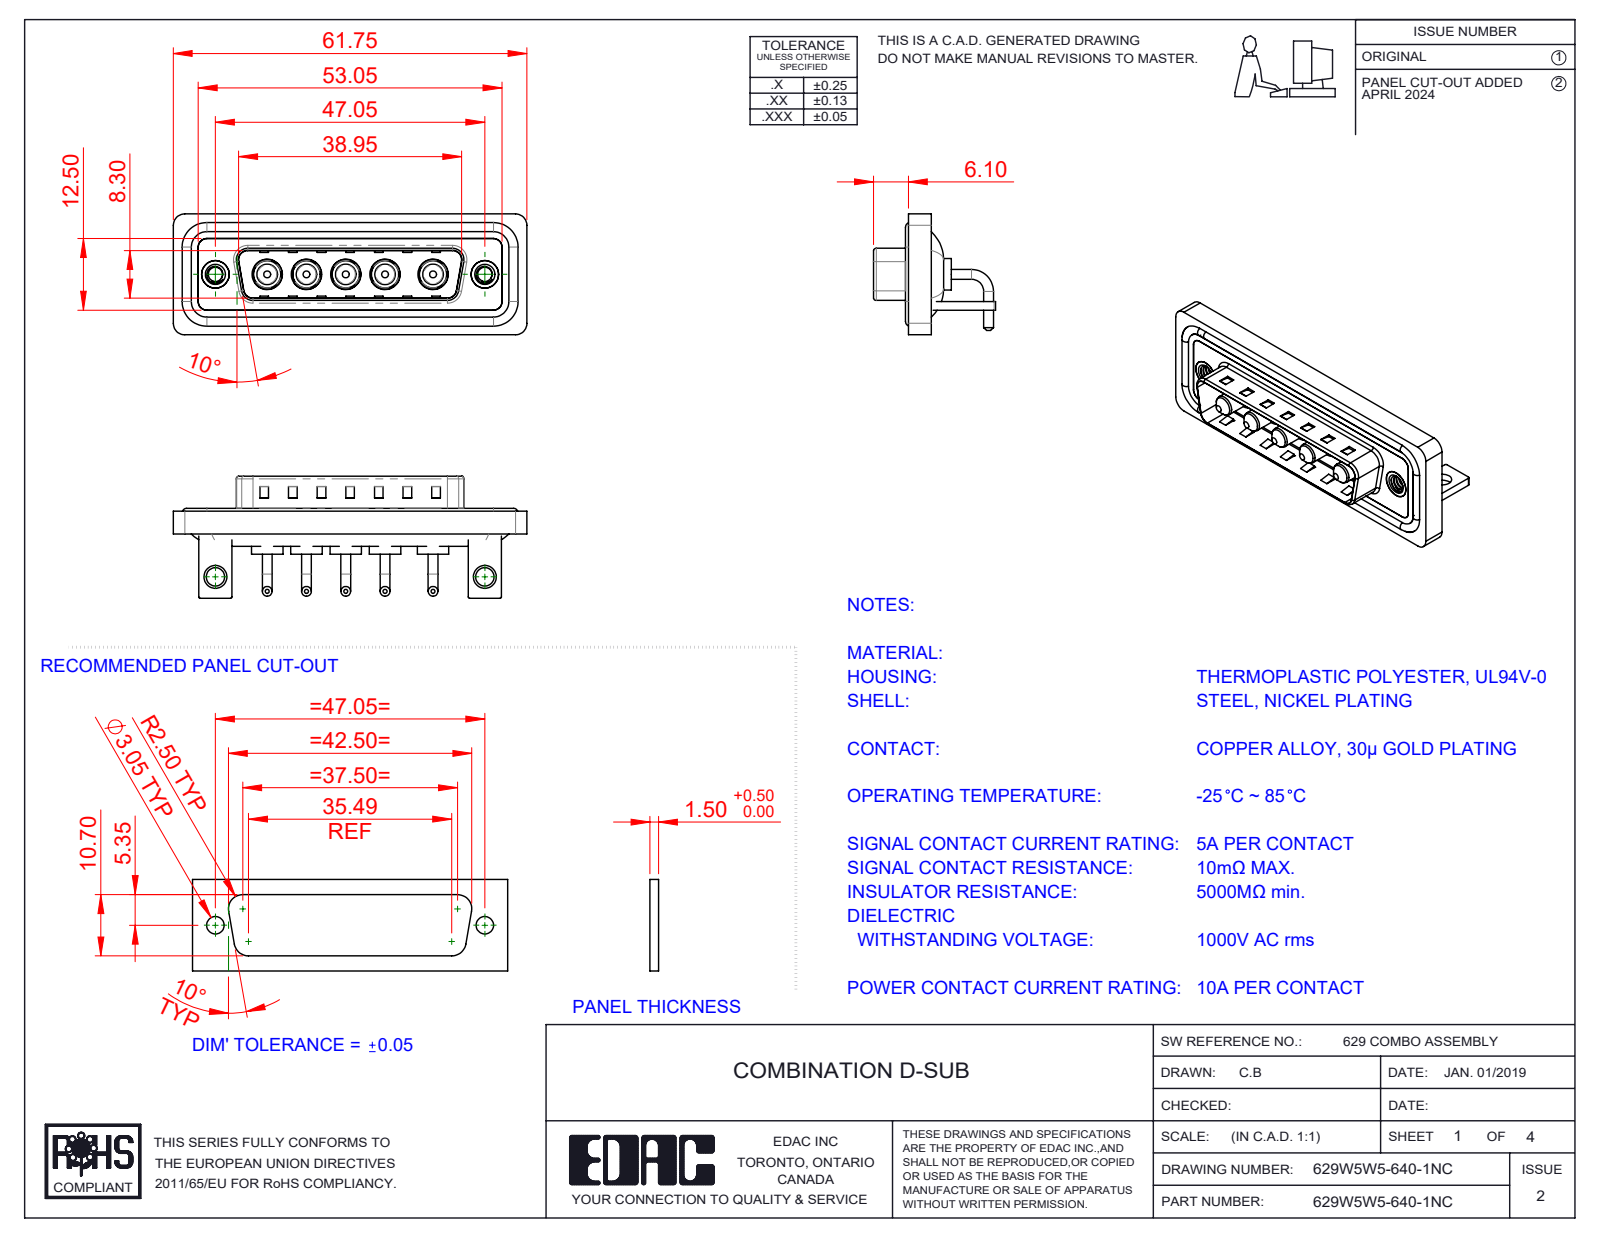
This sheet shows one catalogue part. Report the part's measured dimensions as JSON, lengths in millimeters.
{"part_name": "629Combo Stabilizer Bracket; 629Combo Housing_5W5; 629Combo Shell Rear_25 Contacts; 629W5W5-640-1NC (+4 more)", "step_written_by": "SolidWorks 2023 (CONFIG_CONTROL_DESIGN)", "units": "millimeters", "bodies": {"solids": 19, "faces": 736, "planar": 279, "cylindrical": 311, "other": 146}, "overall_size": [61.75, 21.3, 21.1], "volume_mm3": 7784, "surface_area_mm2": 12605, "round_holes": [[4.85, 5], [5.3, 5], [2.5, 2], [3.2, 2], [4, 2], [4.8, 2], [5, 2]], "round_bosses_or_shafts": [[1.7, 10], [5.5, 5], [5.2, 5], [4.75, 5], [3.75, 5], [3.6, 5], [1.6, 4], [4.9, 2]], "partial_cylinders_radius": [[2, 19], [1.5, 18], [0.25, 16], [0.5, 9], [1.6, 8], [2.1, 5], [0.6, 4], [0.65, 4]], "face_to_face_distances": [0.4, 1.5, 2.9, 0.8, 2.1, 3.7, 1.1, 4.5, 4.1, 1.2], "hole_center_spacings": [6.86, 13.73, 47.05, 6.85, 6.87, 8.37, 8.38, 9.04]}
